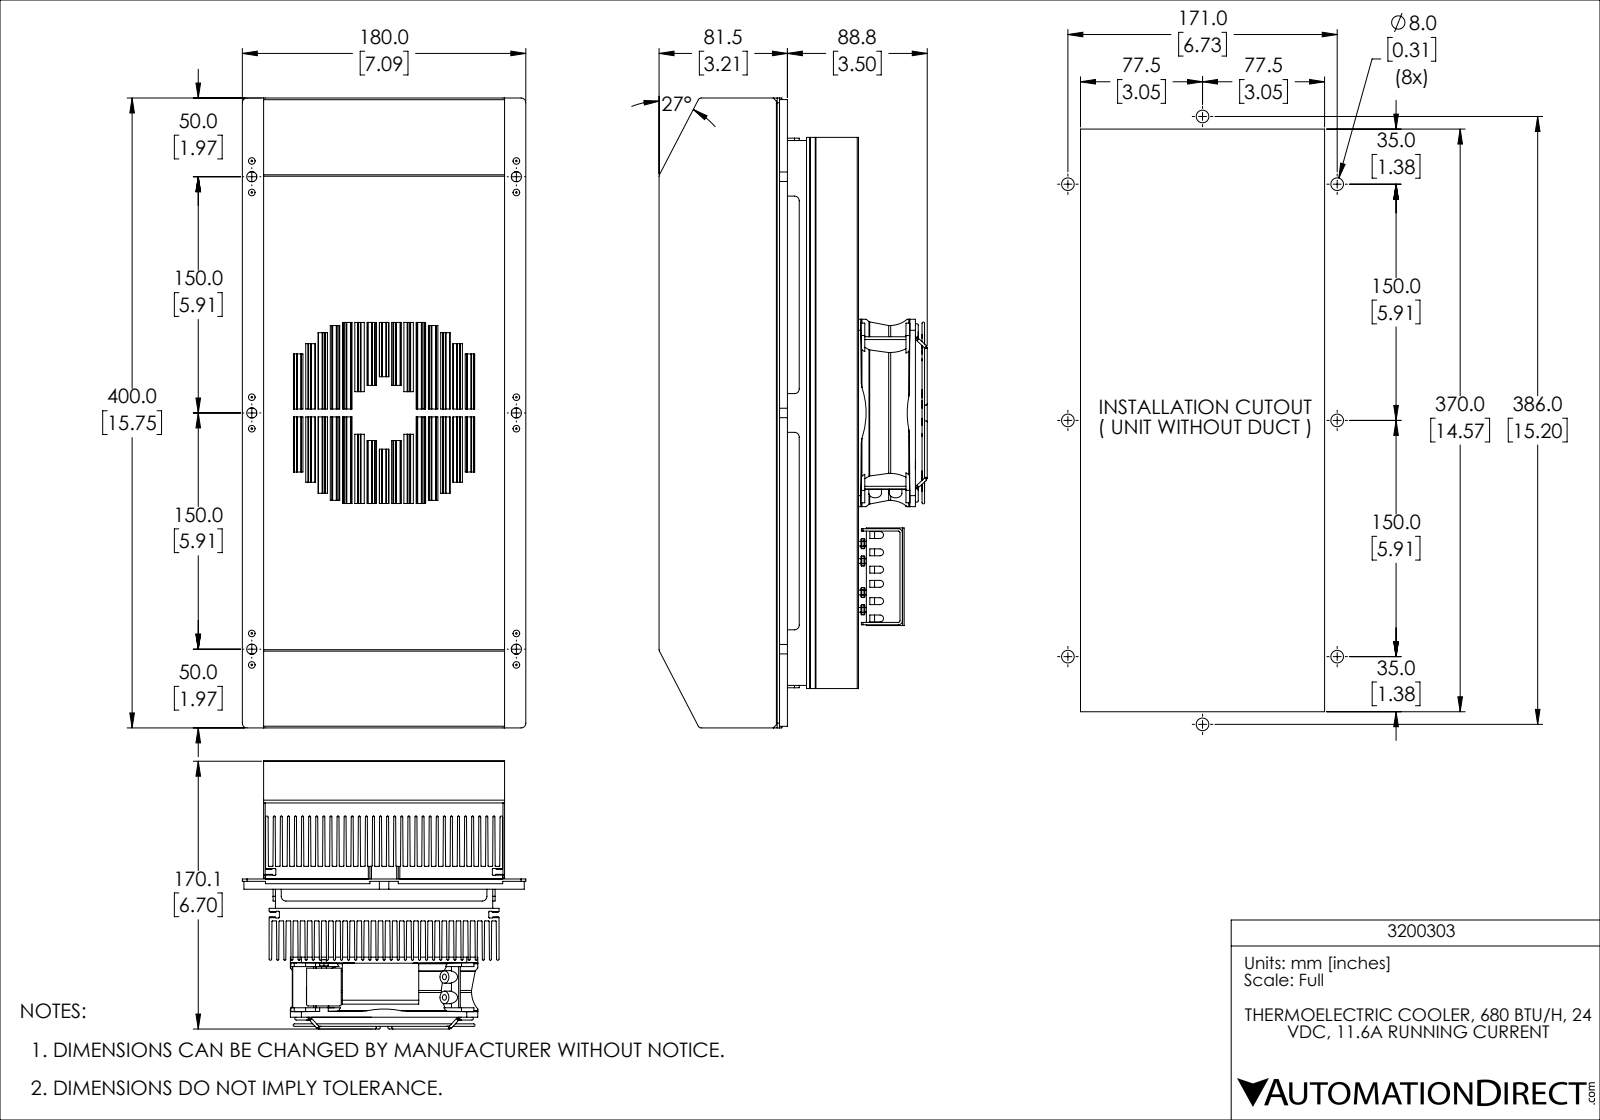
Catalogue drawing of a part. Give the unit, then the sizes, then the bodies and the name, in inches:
Units: inches
Overall size (bounding box): 15.748 × 7.087 × 6.704
Round holes (diameter × count): ⌀0.236 ×14, ⌀0.165 ×12, ⌀0.177 ×8, ⌀0.256 ×8, ⌀0.394 ×8, ⌀0.126 ×4, ⌀0.146 ×4, ⌀0.244 ×4, ⌀0.142 ×2
Round bosses / shafts (diameter × count): ⌀0.071 ×12, ⌀0.236 ×4, ⌀0.118 ×4, ⌀0.098 ×4, ⌀0.315 ×2
Partial cylindrical surfaces — rounded edges, fillets, slot ends (radius × count): R0.012 ×133, R0.024 ×63, R0.02 ×47, R0.118 ×42, R0.039 ×28, R0.197 ×10, R0.087 ×6, R0.031 ×4
Main face-to-face distances: 0.177, 0.354, 0.531, 0.709, 1.063, 0.886, 1.417, 1.24, 1.772, 1.594
Hole centre spacings: 5.906, 0.278, 0.289, 0.447, 0.568, 0.686, 1.22, 0.35
Volume: 203.7 in³ · Surface area: 3 218 in²
Bodies: 8 solids, 2055 faces (1278 planar, 608 cylindrical, 169 other)
Part name (STEP PRODUCT): 3200303
STEP written by: SolidWorks 2019 (AUTOMOTIVE_DESIGN)
